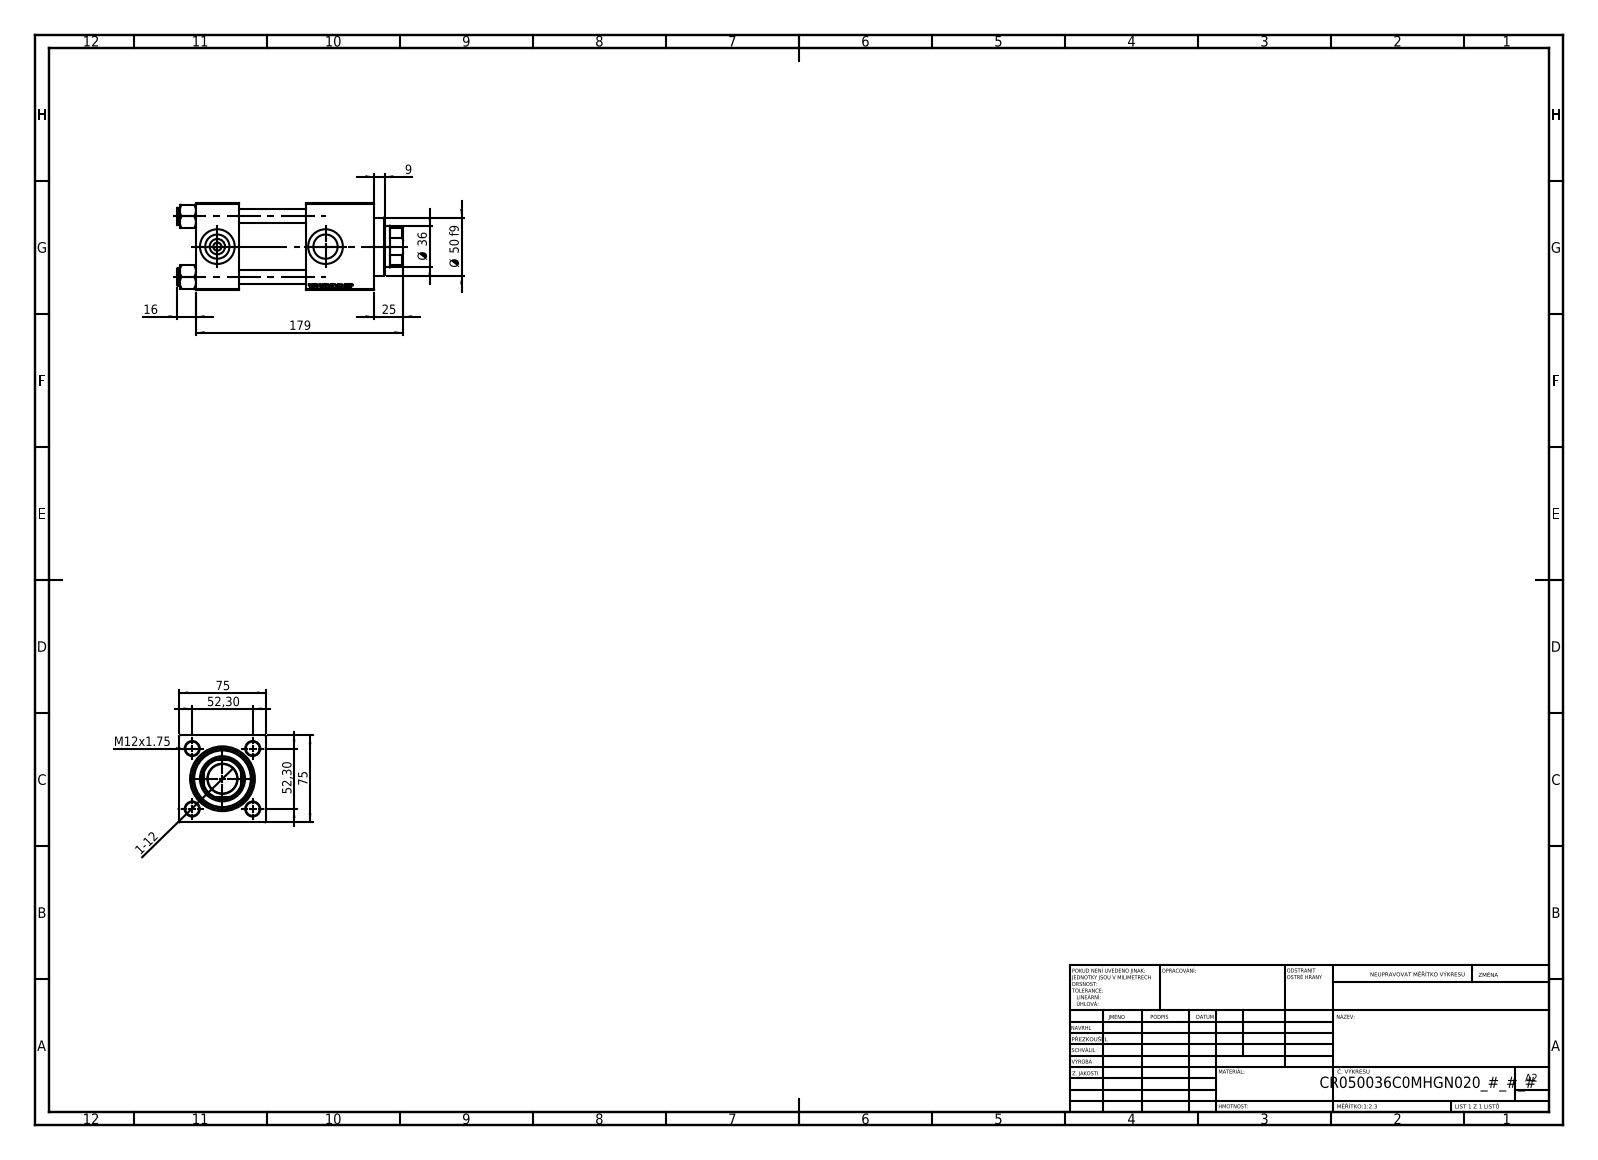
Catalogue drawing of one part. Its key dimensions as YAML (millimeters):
part_name: "V215CR_C_TYCINKA; V215CR_C_Body; V215_VC_A; NUT_M5_C (+1 more)"
step_written_by: "SolidWorks 2019 (CONFIG_CONTROL_DESIGN)"
units: millimeters
bodies: {solids: 11, faces: 1148, planar: 526, cylindrical: 86, other: 536}
overall_size: [195, 75.54, 75]
volume: 686044
surface_area: 155490
round_holes:
  - {diameter: 12, count: 4}
  - {diameter: 7, count: 2}
  - {diameter: 20.96, count: 2}
  - {diameter: 30, count: 2}
  - {diameter: 25.5, count: 1}
  - {diameter: 36, count: 1}
  - {diameter: 39, count: 1}
  - {diameter: 41, count: 1}
  - {diameter: 53, count: 1}
round_bosses_or_shafts:
  - {diameter: 15, count: 4}
  - {diameter: 56, count: 1}
  - {diameter: 50, count: 1}
partial_cylinders:
  - {radius: 17.5, count: 1}
face_to_face_distances: [75, 37, 95, 58, 154, 117, 59, 125.3, 88.3, 30.3]
hole_center_spacings: [36.98, 52.3, 73.96, 93.5]
